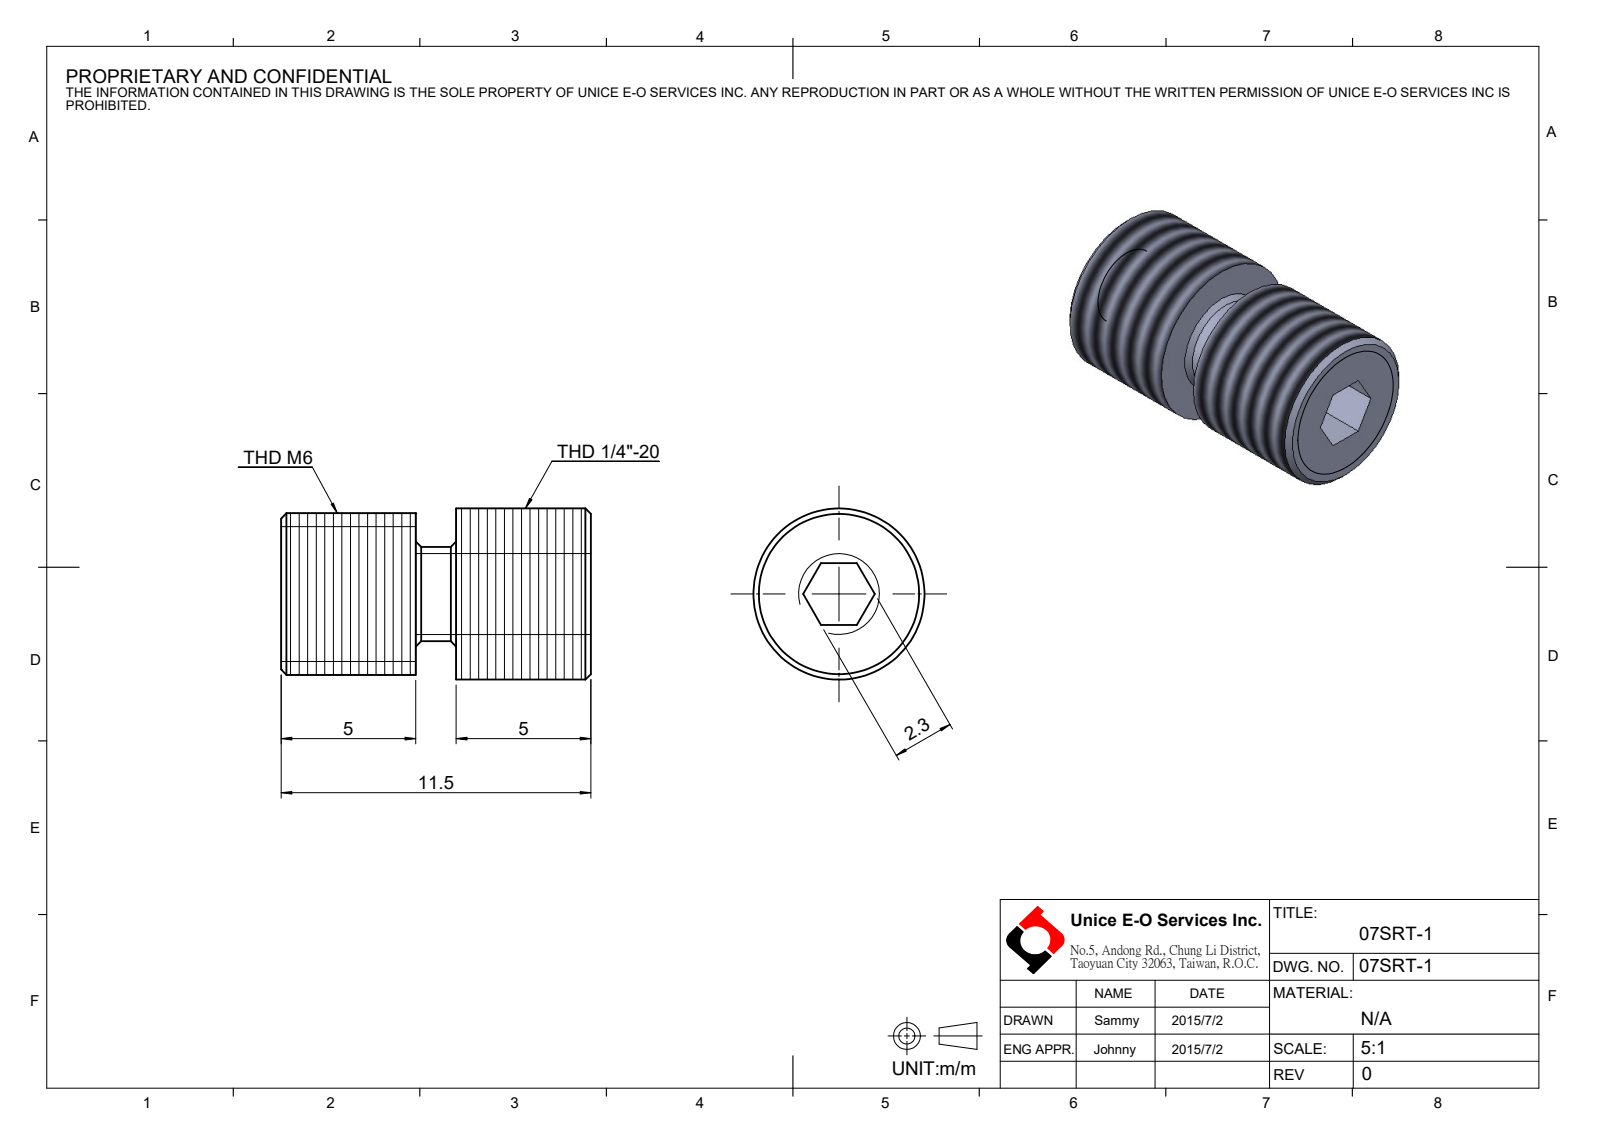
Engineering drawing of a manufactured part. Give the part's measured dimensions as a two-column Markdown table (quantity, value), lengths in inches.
| quantity | value |
| --- | --- |
| part name | 07SRT-1 |
| STEP written by | SolidWorks 2016 (CONFIG_CONTROL_DESIGN) |
| units | inches |
| bodies | 1 solid, 32 faces (18 planar, 6 cylindrical, 8 other) |
| overall size | 0.453 × 0.25 × 0.25 |
| volume | 0.017 in³ |
| surface area | 0.546 in² |
| round bosses / shafts (diameter × count) | 0.25 × 1, 0.236 × 1, 0.138 × 1 |
| main face-to-face distances | 0.197, 0.256, 0.091, 0.453, 0.059, 0.118, 0.335, 0.079, 0.138, 0.217 |
